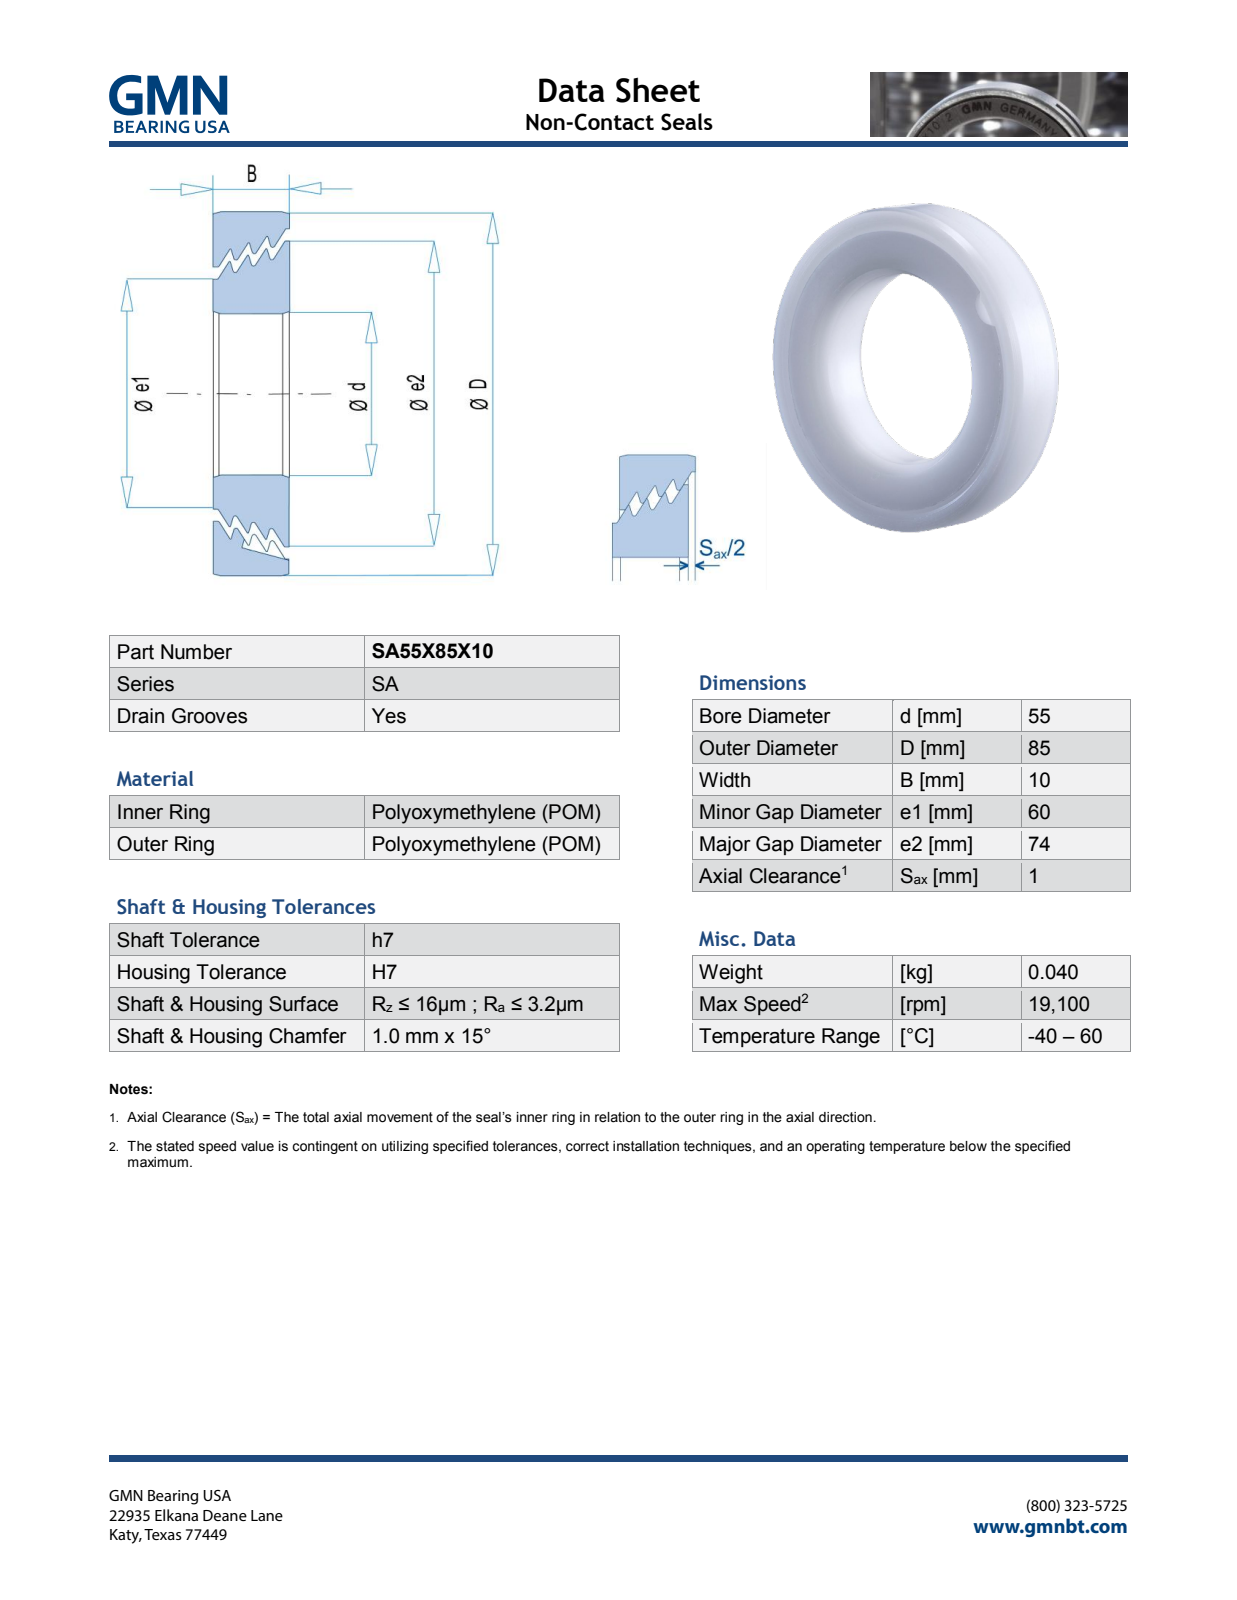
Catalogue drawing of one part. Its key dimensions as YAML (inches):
part_name: "SA55X85X10_PRT"
step_written_by: "PRO/ENGINEER BY PARAMETRIC TECHNOLOGY CORPORATION, 2013150 (AUTOMOTIVE_DESIGN)"
units: inches
bodies: {solids: 2, faces: 692, planar: 619, cylindrical: 13, other: 60}
overall_size: [3.346, 3.346, 0.396]
volume: 1.897
surface_area: 29.35
round_holes:
  - {diameter: 2.165, count: 1}
  - {diameter: 2.426, count: 1}
  - {diameter: 2.978, count: 1}
round_bosses_or_shafts:
  - {diameter: 3.346, count: 1}
  - {diameter: 2.913, count: 1}
  - {diameter: 2.362, count: 1}
partial_cylinders:
  - {radius: 0.236, count: 1}
face_to_face_distances: [0.394, 0.396, 0.215, 0.212, 0.181, 0.013, 0.013, 0.102, 0.089, 0.072]
